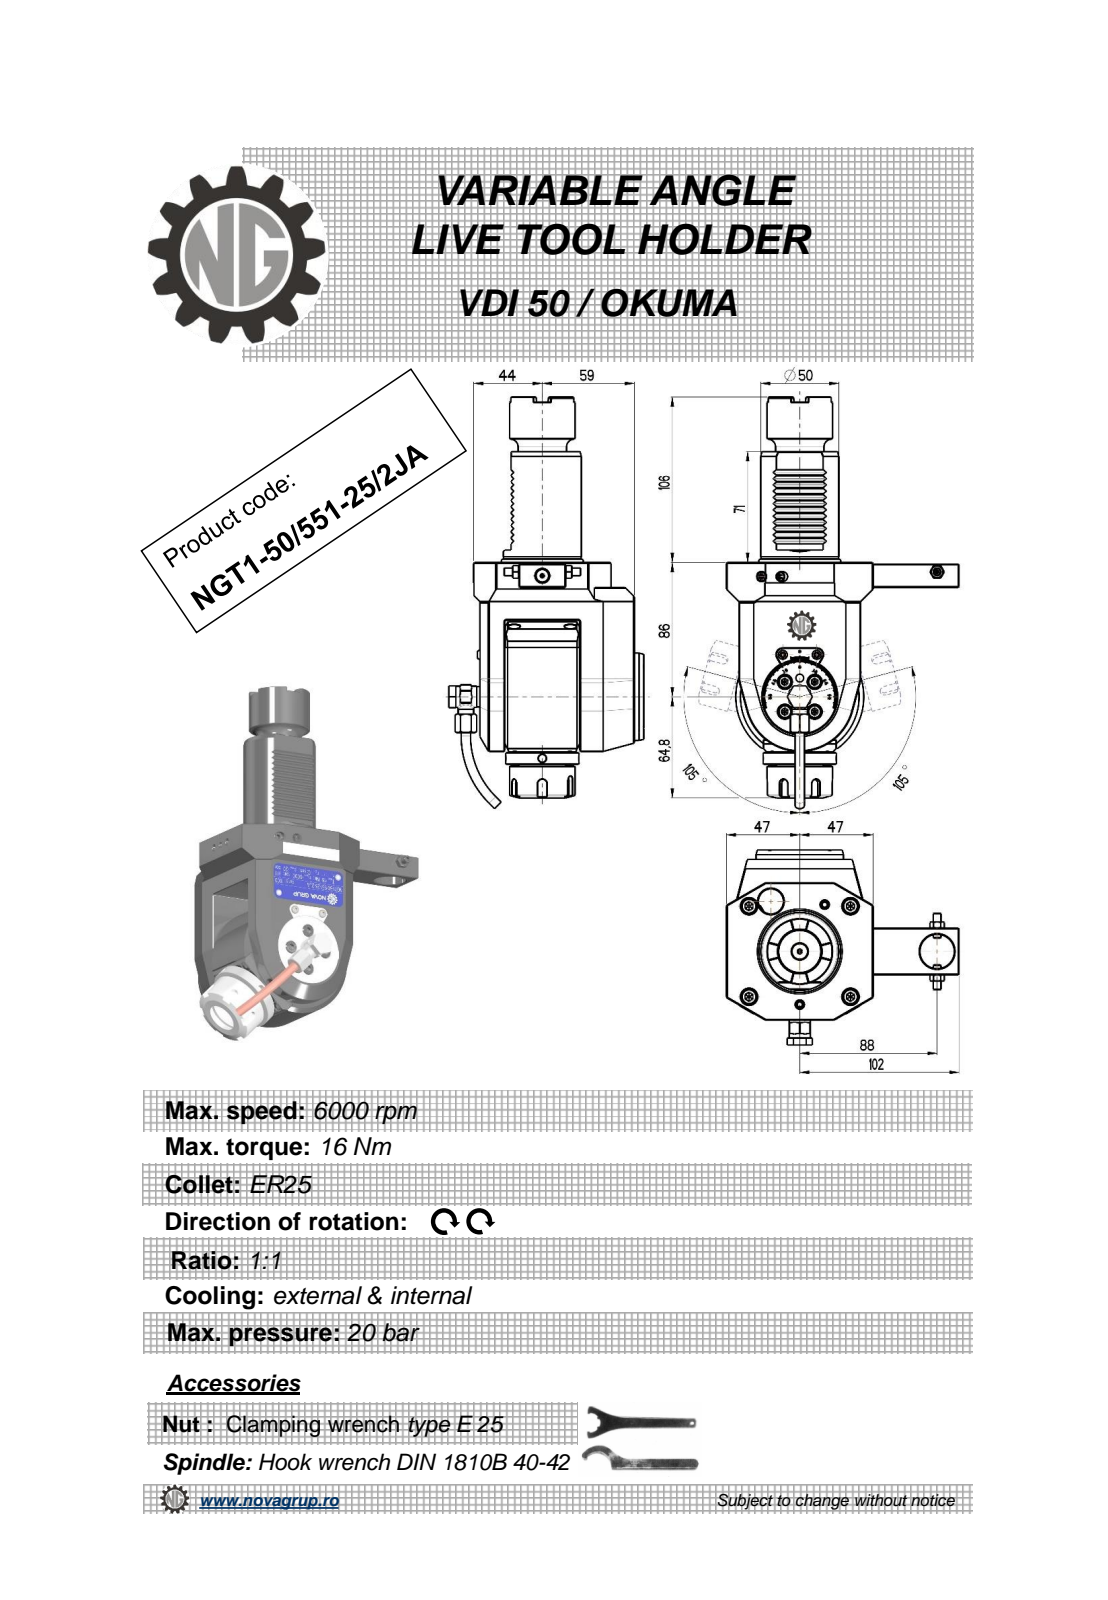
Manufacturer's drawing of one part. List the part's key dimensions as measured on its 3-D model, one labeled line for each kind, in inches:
Part name (STEP PRODUCT): NGT1_50_551_25_2JA
STEP written by: PRO/ENGINEER BY PARAMETRIC TECHNOLOGY CORPORATION, 2010280 (CONFIG_CONTROL_DESIGN)
Units: inches
Bodies: 1 solid, 666 faces (286 planar, 144 cylindrical, 236 other)
Overall size (bounding box): 10.381 × 5.866 × 4.917
Volume: 65.36 in³ · Surface area: 151.5 in²
Round holes (diameter × count): ⌀0.157 ×3, ⌀0.197 ×2, ⌀0.118 ×1, ⌀0.244 ×1, ⌀0.354 ×1, ⌀0.374 ×1, ⌀0.433 ×1, ⌀0.799 ×1, ⌀0.866 ×1, ⌀1.102 ×1
Round bosses / shafts (diameter × count): ⌀0.394 ×2, ⌀0.236 ×2, ⌀0.224 ×2, ⌀2.205 ×1, ⌀1.969 ×1, ⌀1.85 ×1, ⌀1.654 ×1, ⌀1.378 ×1
Partial cylindrical surfaces — rounded edges, fillets, slot ends (radius × count): R0.01 ×12, R0.012 ×12, R0.006 ×6, R0.118 ×5, R0.02 ×4, R0.039 ×2, R0.394 ×2, R0.303 ×1
Main face-to-face distances: 1.457, 0.63, 3.898, 0.827, 0.236, 0.315, 2.52, 4.134, 0.787, 1.378
Hole centre spacings: 0.016, 1.553, 1.929, 1.945, 3.465, 3.965, 3.973, 4.604
